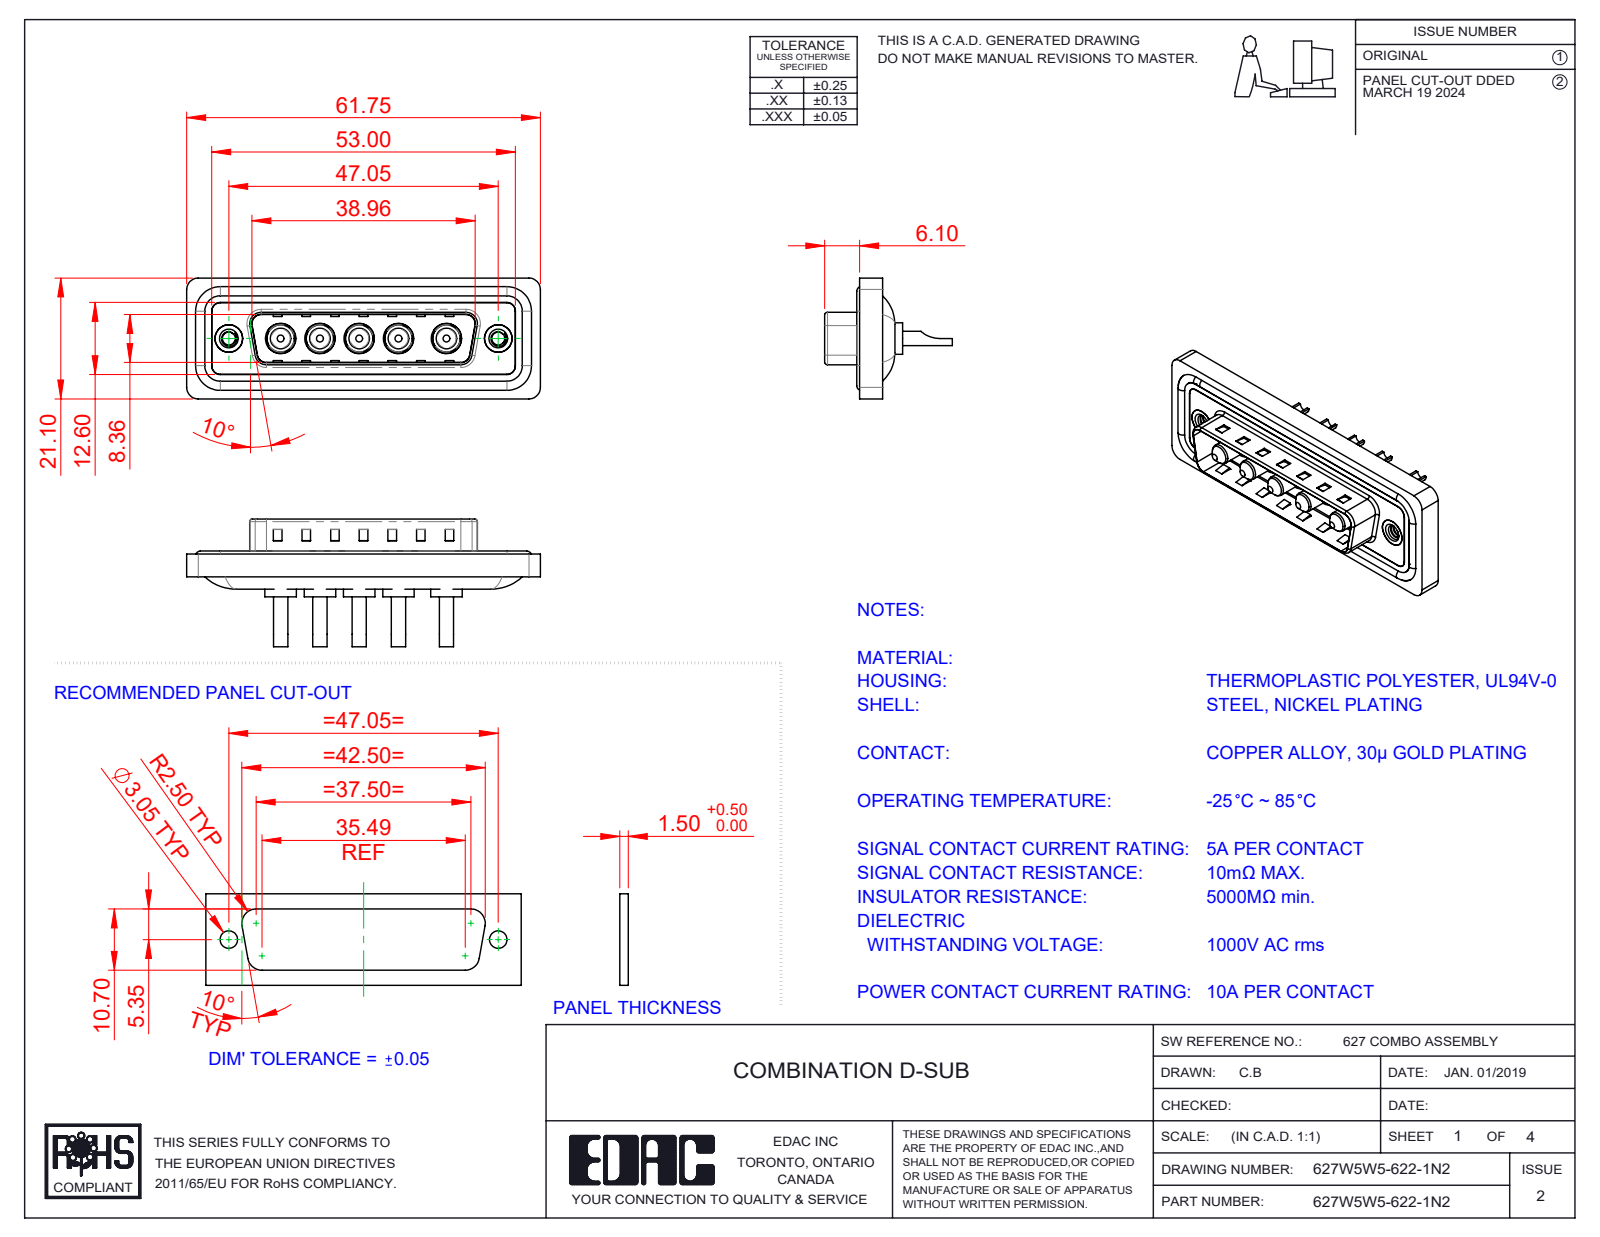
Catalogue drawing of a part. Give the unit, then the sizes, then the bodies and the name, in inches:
Units: inches
Overall size (bounding box): 2.431 × 0.878 × 0.831
Round holes (diameter × count): ⌀0.067 ×5, ⌀0.191 ×5, ⌀0.209 ×5, ⌀0.089 ×2, ⌀0.157 ×2, ⌀0.189 ×2, ⌀0.197 ×2
Round bosses / shafts (diameter × count): ⌀0.217 ×5, ⌀0.205 ×5, ⌀0.187 ×5, ⌀0.148 ×5, ⌀0.142 ×5, ⌀0.098 ×5, ⌀0.063 ×4, ⌀0.193 ×2
Partial cylindrical surfaces — rounded edges, fillets, slot ends (radius × count): R0.059 ×22, R0.079 ×18, R0.02 ×8, R0.063 ×8, R0.083 ×5, R0.01 ×4, R0.024 ×4, R0.026 ×4
Main face-to-face distances: 0.016, 0.059, 0.02, 0.043, 0.122, 0.063, 0.114, 0.032, 0.377, 0.222
Hole centre spacings: 0.27, 0.356, 0.541, 1.496, 0.27, 0.33, 0.33, 0.356
Volume: 0.455 in³ · Surface area: 18.65 in²
Bodies: 17 solids, 708 faces (269 planar, 298 cylindrical, 141 other)
Part name (STEP PRODUCT): 627Combo Waterproof Housing_25 Contacts; Power Pin_10A SC; 627Combo Threaded Rivet_2; 627Combo Housing_5W5 (+3 more)
STEP written by: SolidWorks 2023 (CONFIG_CONTROL_DESIGN)
